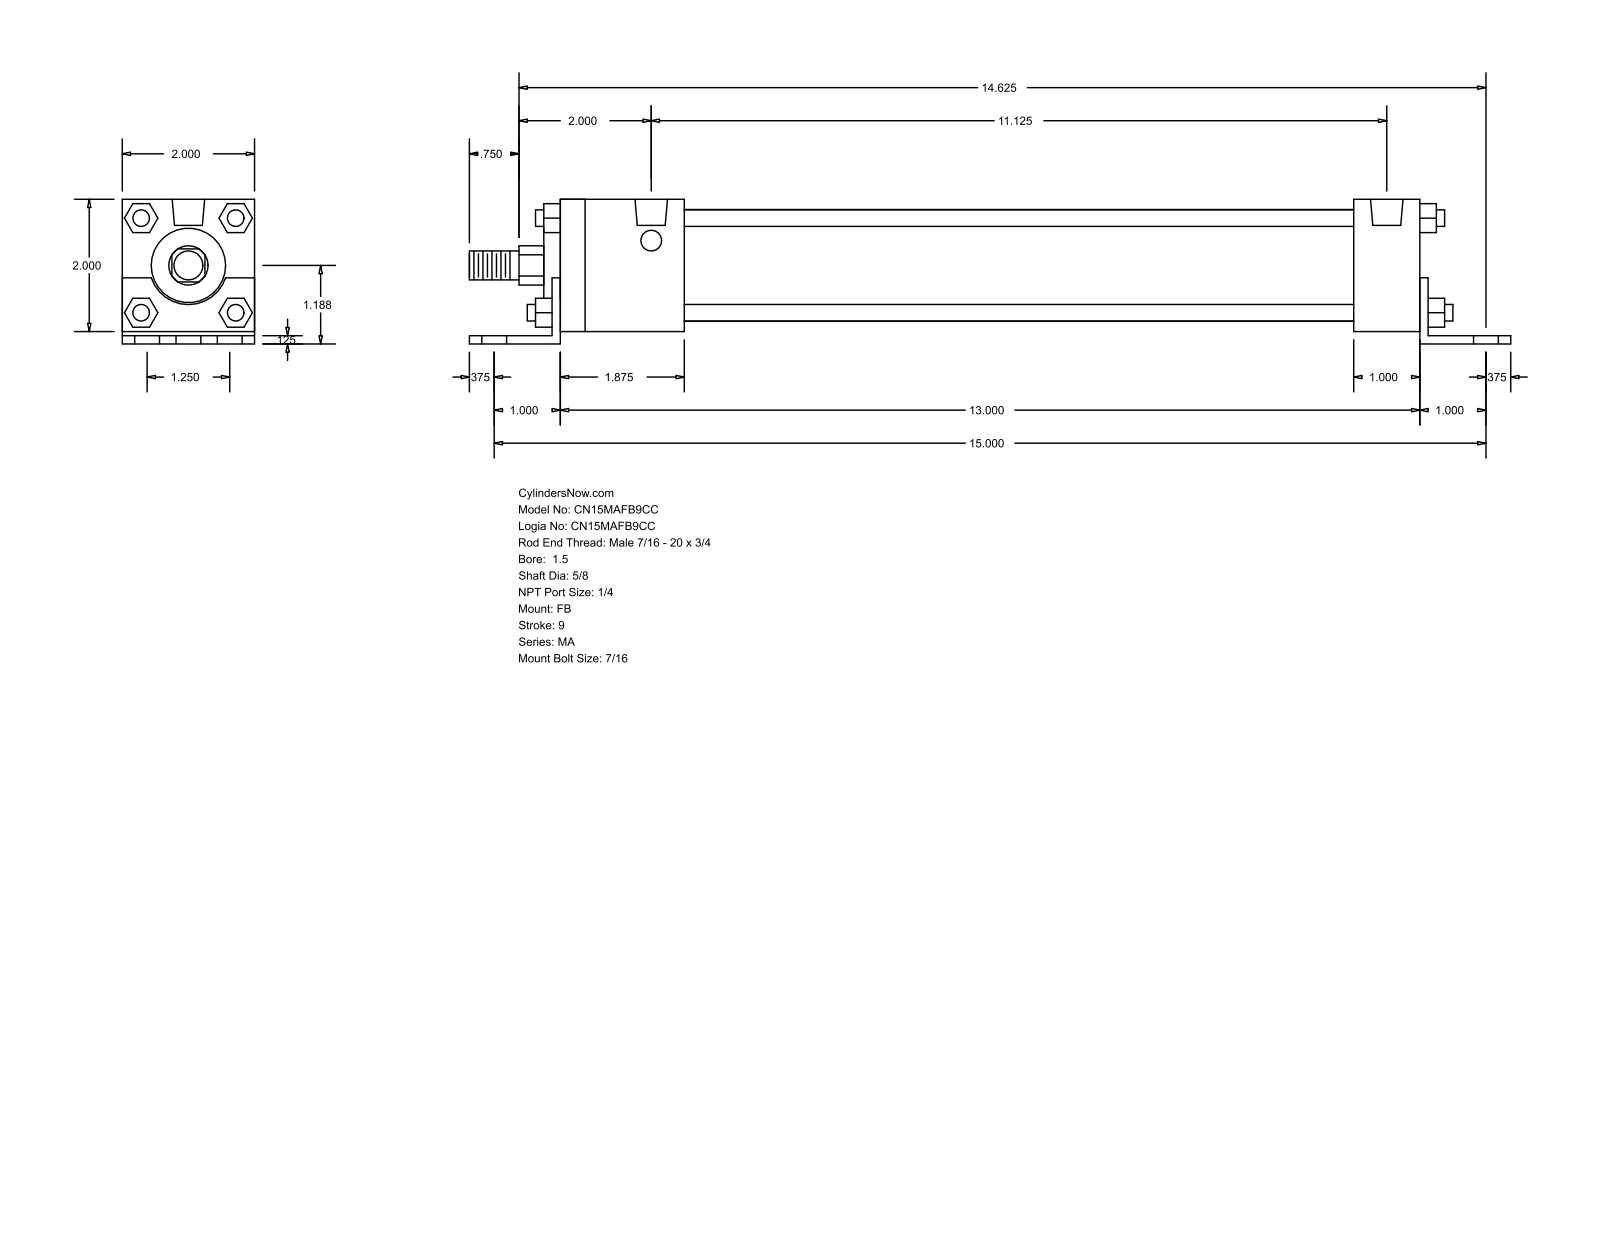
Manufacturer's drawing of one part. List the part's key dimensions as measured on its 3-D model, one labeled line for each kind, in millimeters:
Part name (STEP PRODUCT): MA_FB__0150_0.625
STEP written by: GSSL Pune (CONFIG_CONTROL_DESIGN)
Units: millimetres
Bodies: 0 solids, 140 faces (105 planar, 35 cylindrical, 0 other)
Overall size (bounding box): 400.05 × 55.56 × 50.8
Round holes (diameter × count): ⌀11.11 ×6, ⌀7.94 ×4, ⌀12.49 ×2
Round bosses / shafts (diameter × count): ⌀6.35 ×4, ⌀42.93 ×1, ⌀28.57 ×1, ⌀15.88 ×1, ⌀11.11 ×1
Partial cylindrical surfaces — rounded edges, fillets, slot ends (radius × count): R7.54 ×1, R15.05 ×1
Main face-to-face distances: 50.8, 3.17, 4.76, 55.56, 1.59, 52.39, 3.18, 333.37, 330.19, 6.35
Hole centre spacings: 15.88, 381.34, 381.01, 31.76, 41.28, 62.38, 282.58, 321.07
